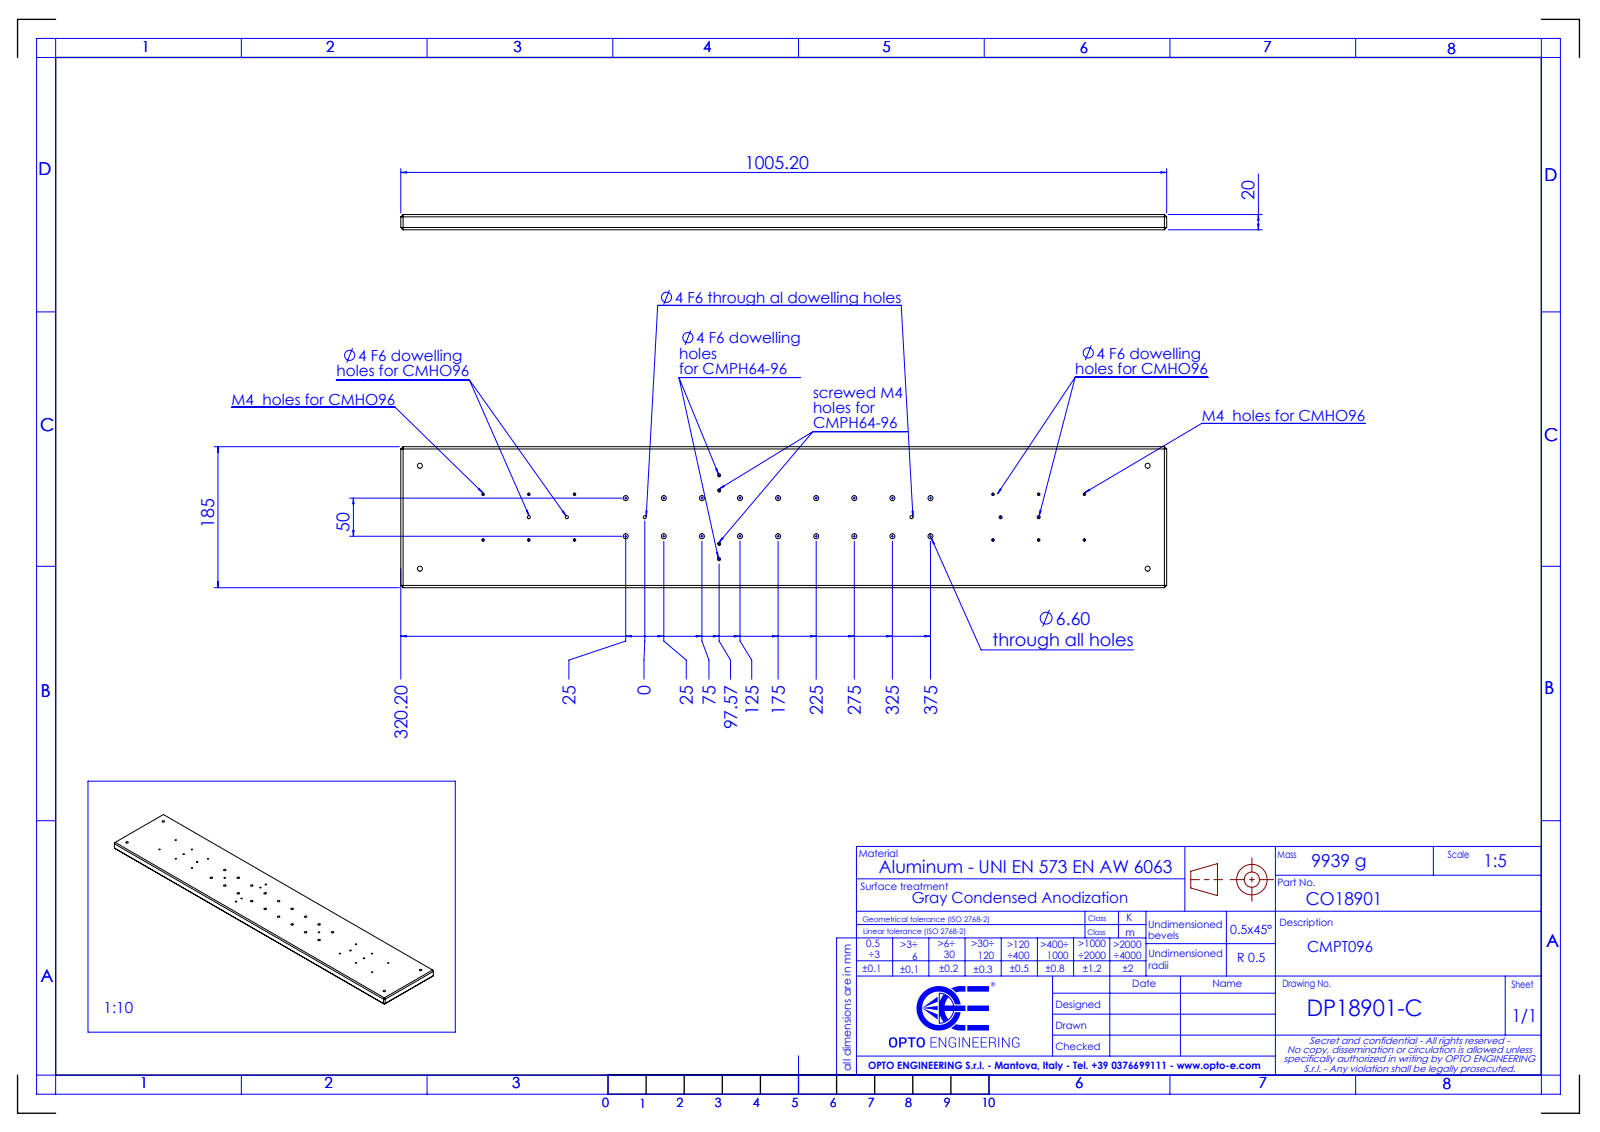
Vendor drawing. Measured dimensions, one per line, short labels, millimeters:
name: DP18901-C_CMPT096
written by: SolidWorks 2021 (AUTOMOTIVE_DESIGN)
unit: mm
bodies: 1 solid, 128 faces (28 planar, 88 cylindrical, 12 other)
size: 1005.2 × 185 × 20
volume: 3 680 000 mm³; area: 421 793 mm²
holes: 22× ⌀6.6, 14× ⌀3.3, 8× ⌀4
face distances: 20, 185, 140.7, 1005.2, 720.57, 837.22, 691.36, 5, 15
hole spacings: 50, 70.71, 100, 111.8, 150, 158.11, 200, 206.16
